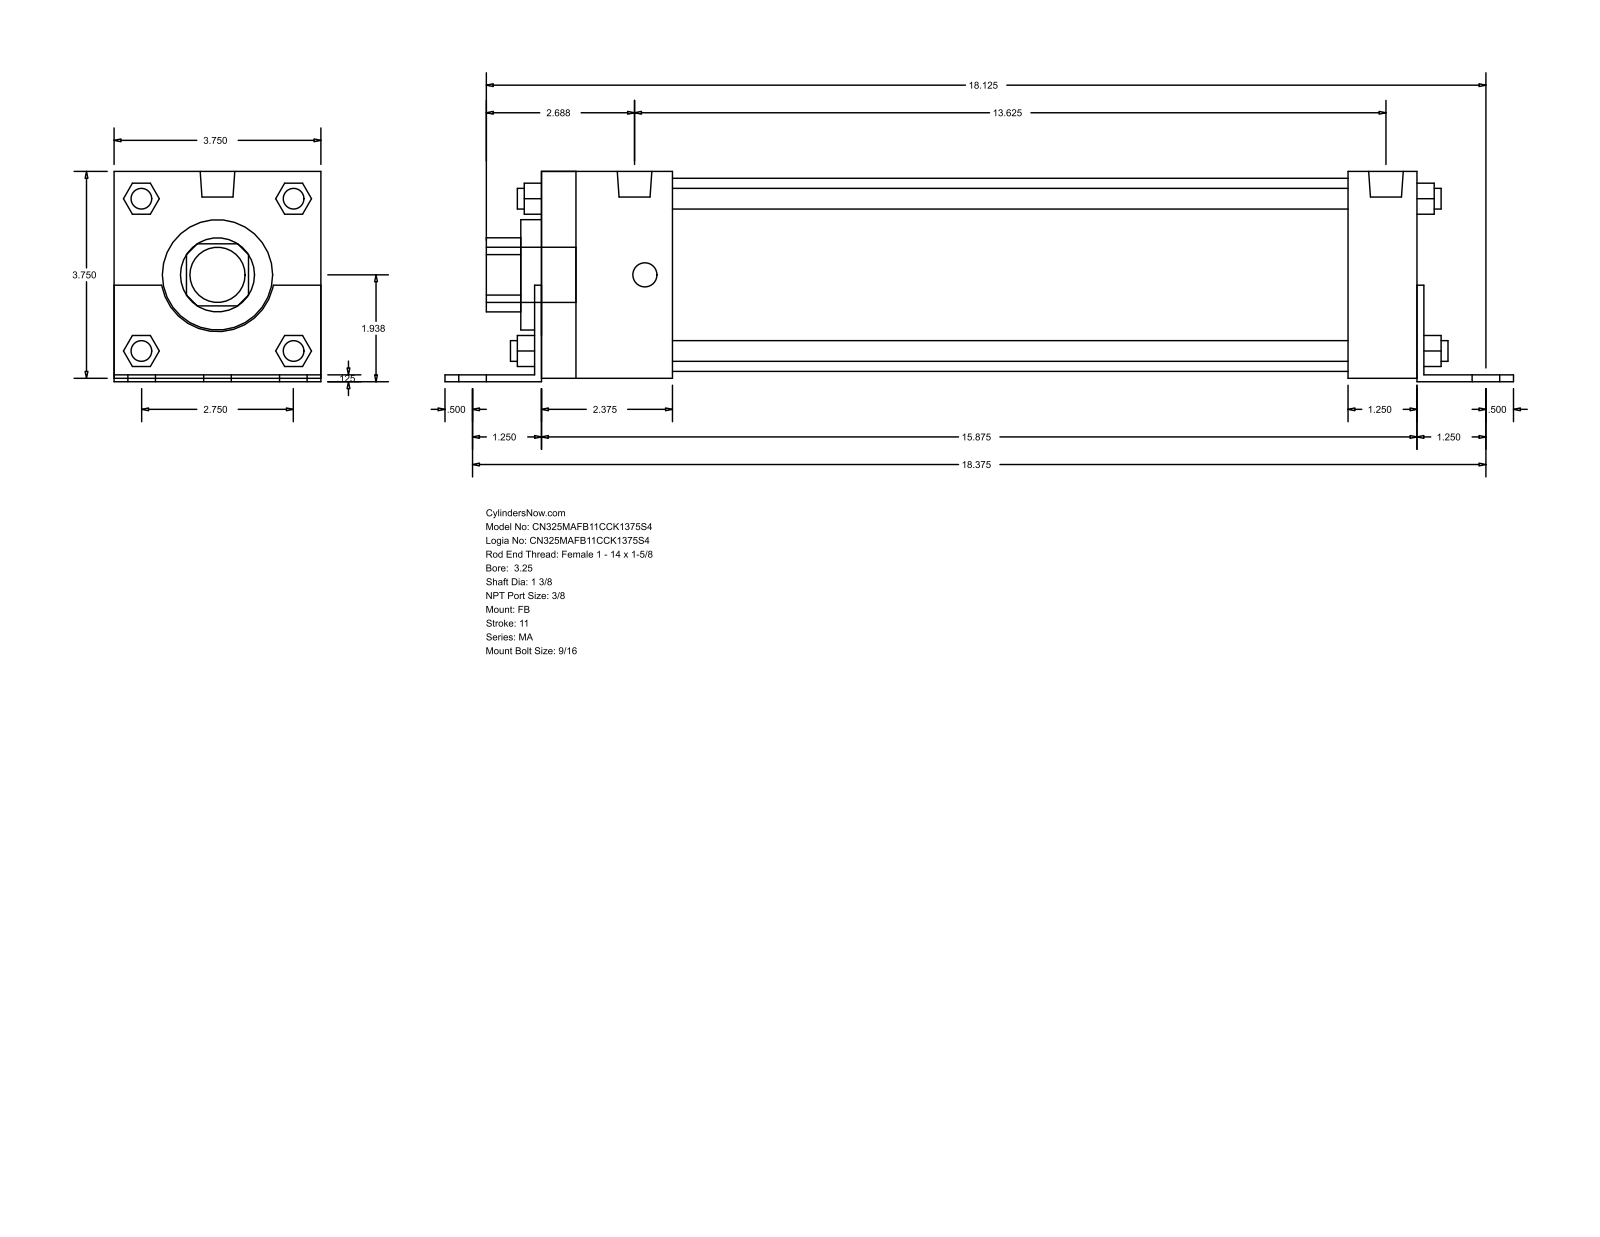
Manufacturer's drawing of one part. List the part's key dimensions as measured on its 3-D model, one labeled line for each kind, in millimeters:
Part name (STEP PRODUCT): MA_FB__0325_1.375
STEP written by: GSSL Pune (CONFIG_CONTROL_DESIGN)
Units: millimetres
Bodies: 0 solids, 140 faces (105 planar, 35 cylindrical, 0 other)
Overall size (bounding box): 492.12 × 96.84 × 95.25
Round holes (diameter × count): ⌀34.92 ×1, ⌀50.8 ×1, ⌀88.9 ×1
Round bosses / shafts (diameter × count): ⌀14.29 ×6, ⌀11.11 ×4, ⌀9.53 ×4, ⌀15.93 ×2, ⌀25.4 ×1
Partial cylindrical surfaces — rounded edges, fillets, slot ends (radius × count): R17.06 ×1, R26.16 ×1
Main face-to-face distances: 95.24, 3.17, 1.59, 96.83, 1.58, 93.66, 3.18, 403.22, 406.4, 60.32
